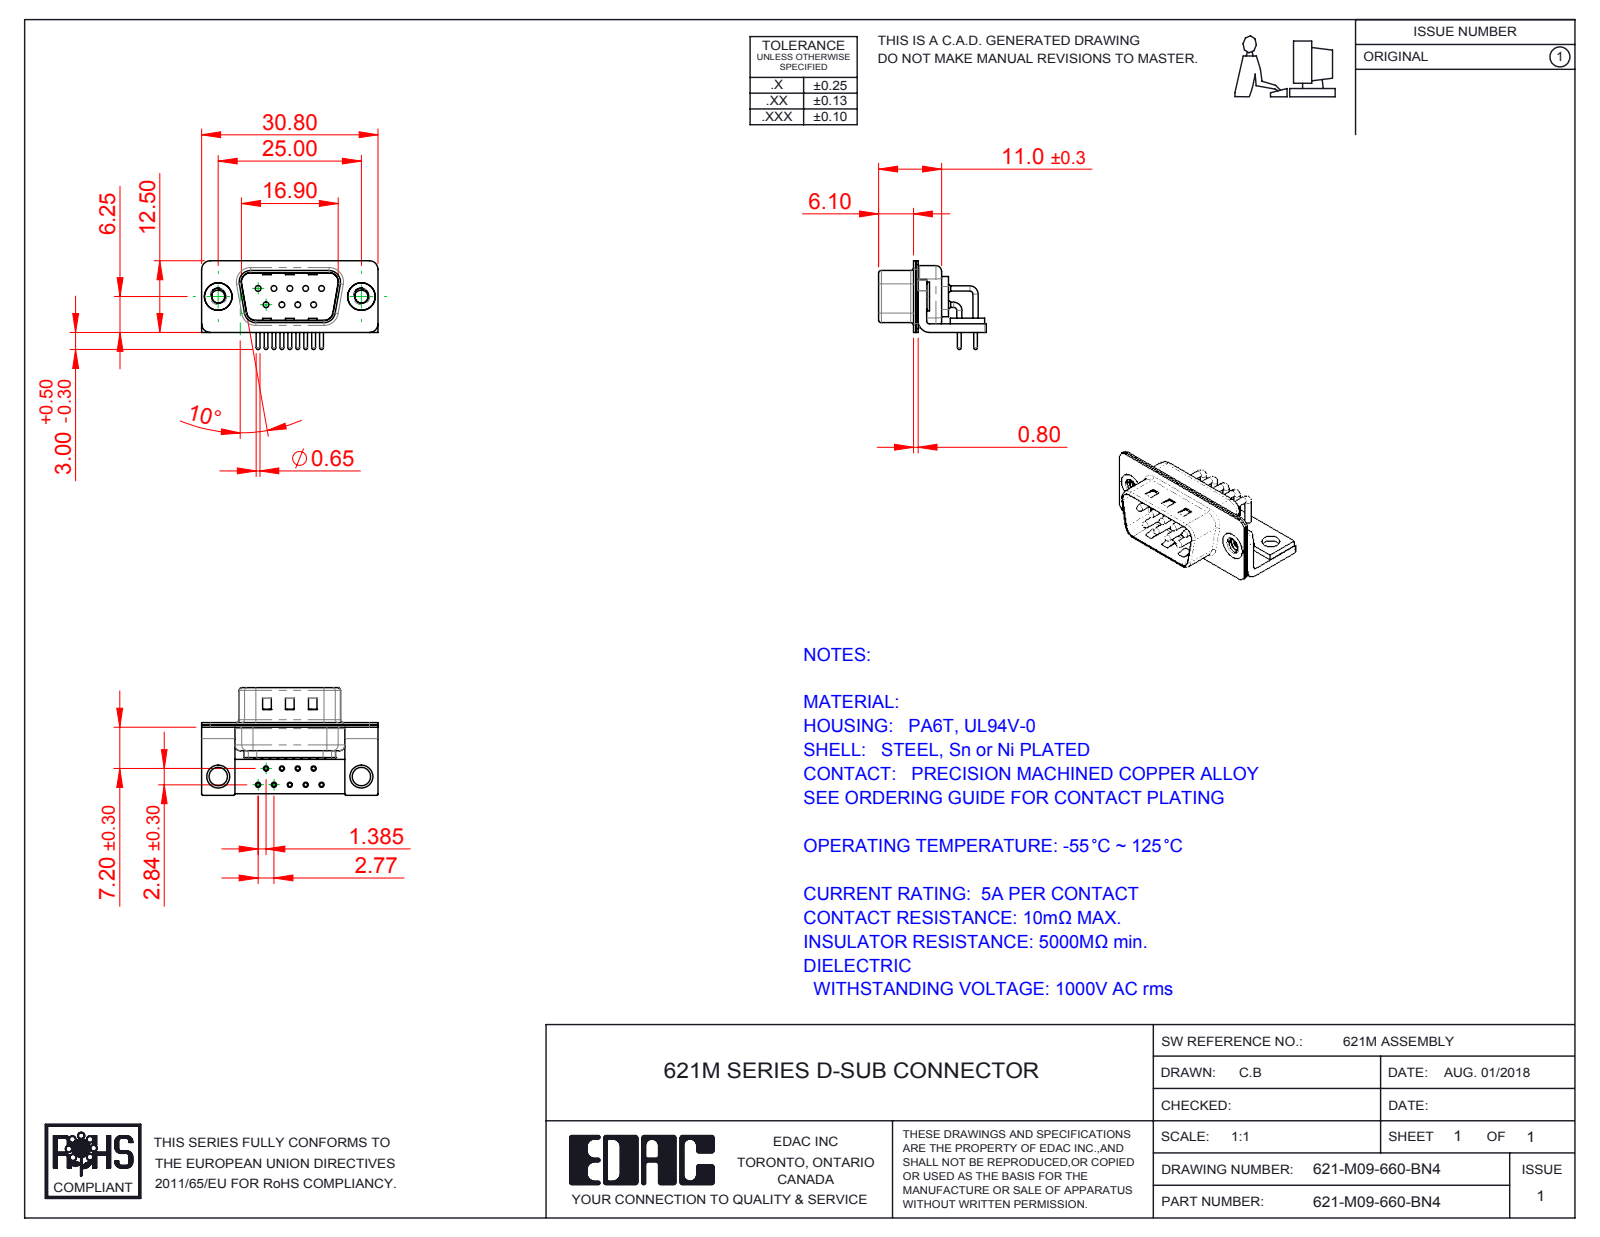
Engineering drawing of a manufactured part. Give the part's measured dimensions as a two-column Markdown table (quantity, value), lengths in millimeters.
| quantity | value |
| --- | --- |
| part name | 621M Shell Front_09 Contacts; 621M 4-40 Threaded Rivet_Stabilizer; 621M Stabilizer Board_09 Contacts; 621M Contact Row 2 (+5 more) |
| STEP written by | SolidWorks 2016 (CONFIG_CONTROL_DESIGN) |
| units | millimeters |
| bodies | 17 solids, 1362 faces (709 planar, 493 cylindrical, 160 other) |
| overall size | 30.8 × 18.8 × 15.49 |
| volume | 1 755 mm³ |
| surface area | 4 812 mm² |
| round holes (diameter × count) | 0.9 × 9, 1 × 9, 1.7 × 9, 2 × 9, 2.26 × 2, 3.2 × 2, 4 × 2, 4.8 × 2 |
| round bosses / shafts (diameter × count) | 1.5 × 9, 0.9 × 9, 0.65 × 9, 5 × 2, 4.9 × 2 |
| partial cylindrical surfaces (radius × count) | 0.25 × 16, 1.5 × 16, 2 × 13, 0.5 × 9, 1.01 × 9, 1.6 × 8, 0.6 × 4, 0.65 × 4 |
| main face-to-face distances | 0.4, 1.5, 0.8, 0.85, 1.25, 1, 10.4, 9.55, 1.9, 2.5 |
| hole center spacings | 3.16, 2.77, 5.54, 5.03, 5.04, 8.31, 7.48, 7.49 |
